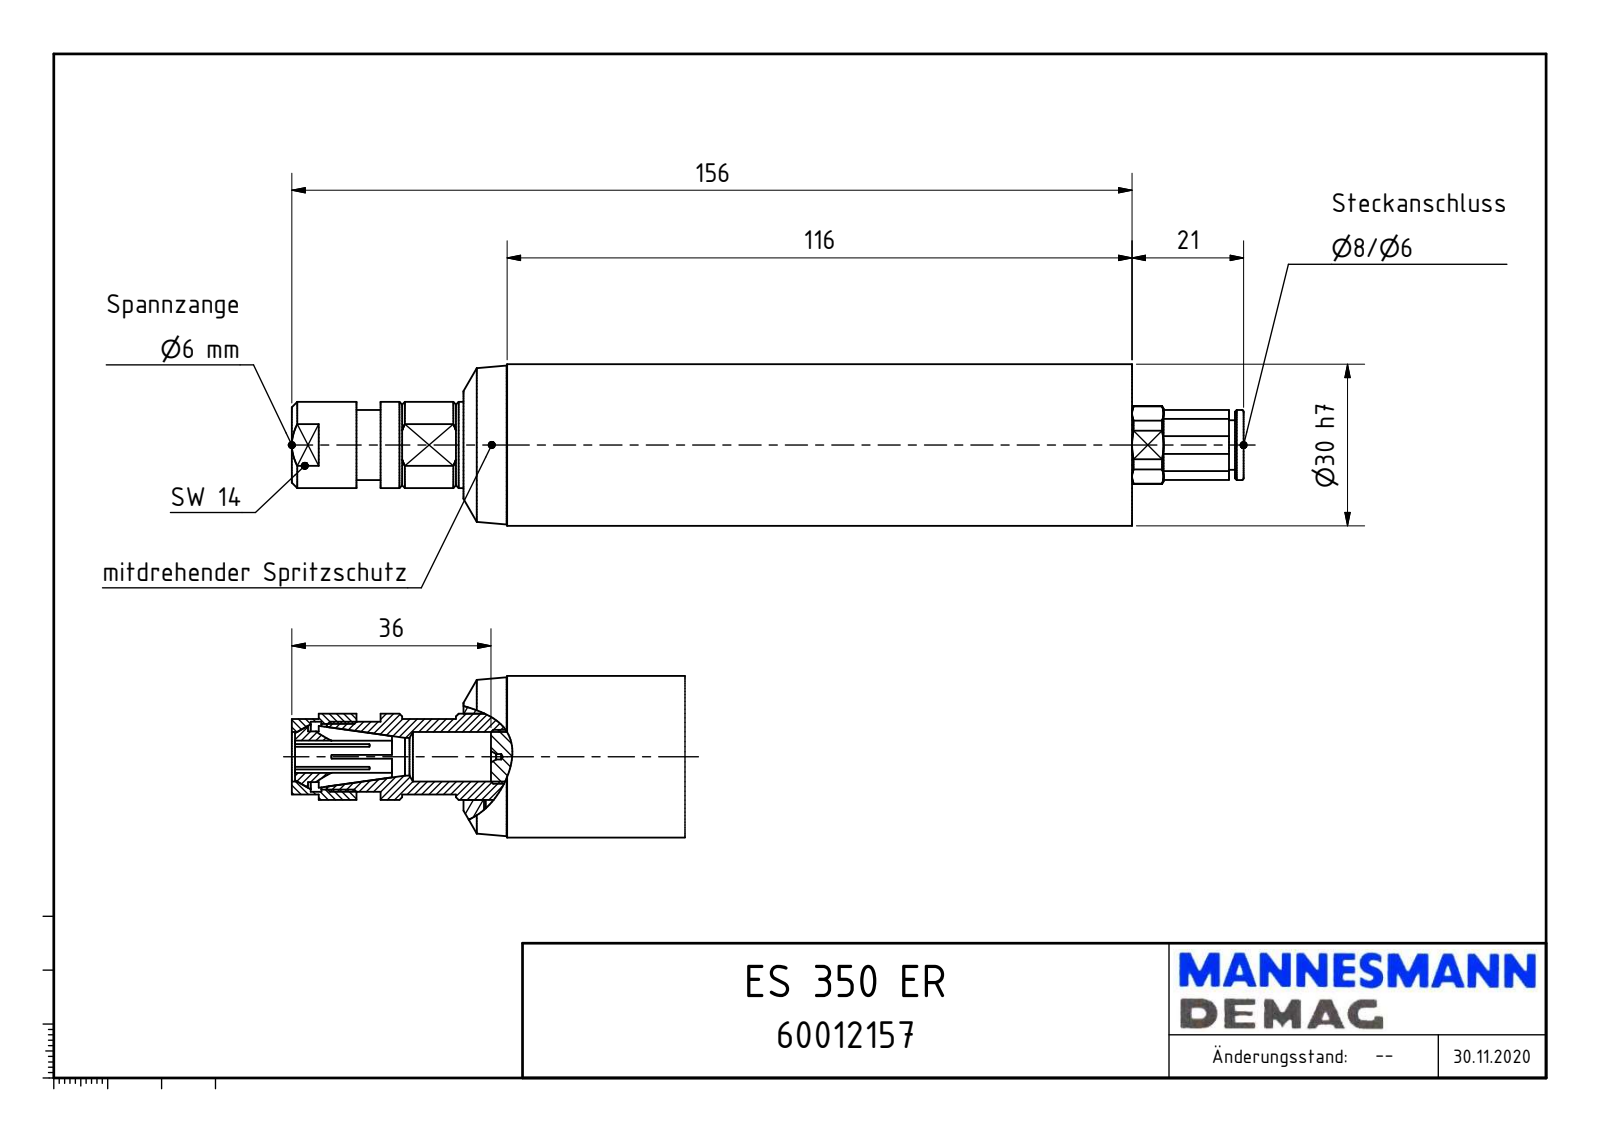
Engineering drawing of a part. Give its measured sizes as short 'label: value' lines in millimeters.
name: ES 350 ER_60012157
written by: Autodesk Inventor 2018 (AUTOMOTIVE_DESIGN)
unit: mm
bodies: 1 solid, 181 faces (89 planar, 43 cylindrical, 49 other)
size: 176.67 × 30 × 30
volume: 93 701 mm³; area: 18 796 mm²
holes: 1× ⌀6, 1× ⌀8, 1× ⌀9.2, 1× ⌀12.19, 1× ⌀24, 1× ⌀25.5, 1× ⌀26.92
bosses: 1× ⌀30, 1× ⌀25, 1× ⌀23.89, 1× ⌀16, 1× ⌀13, 1× ⌀9.4
rounds: 8× R19, 1× R6.75, 1× R7.25
face distances: 0.7, 116, 13, 8.2, 124.2, 14, 6.65, 7.35, 13.5, 6.15
